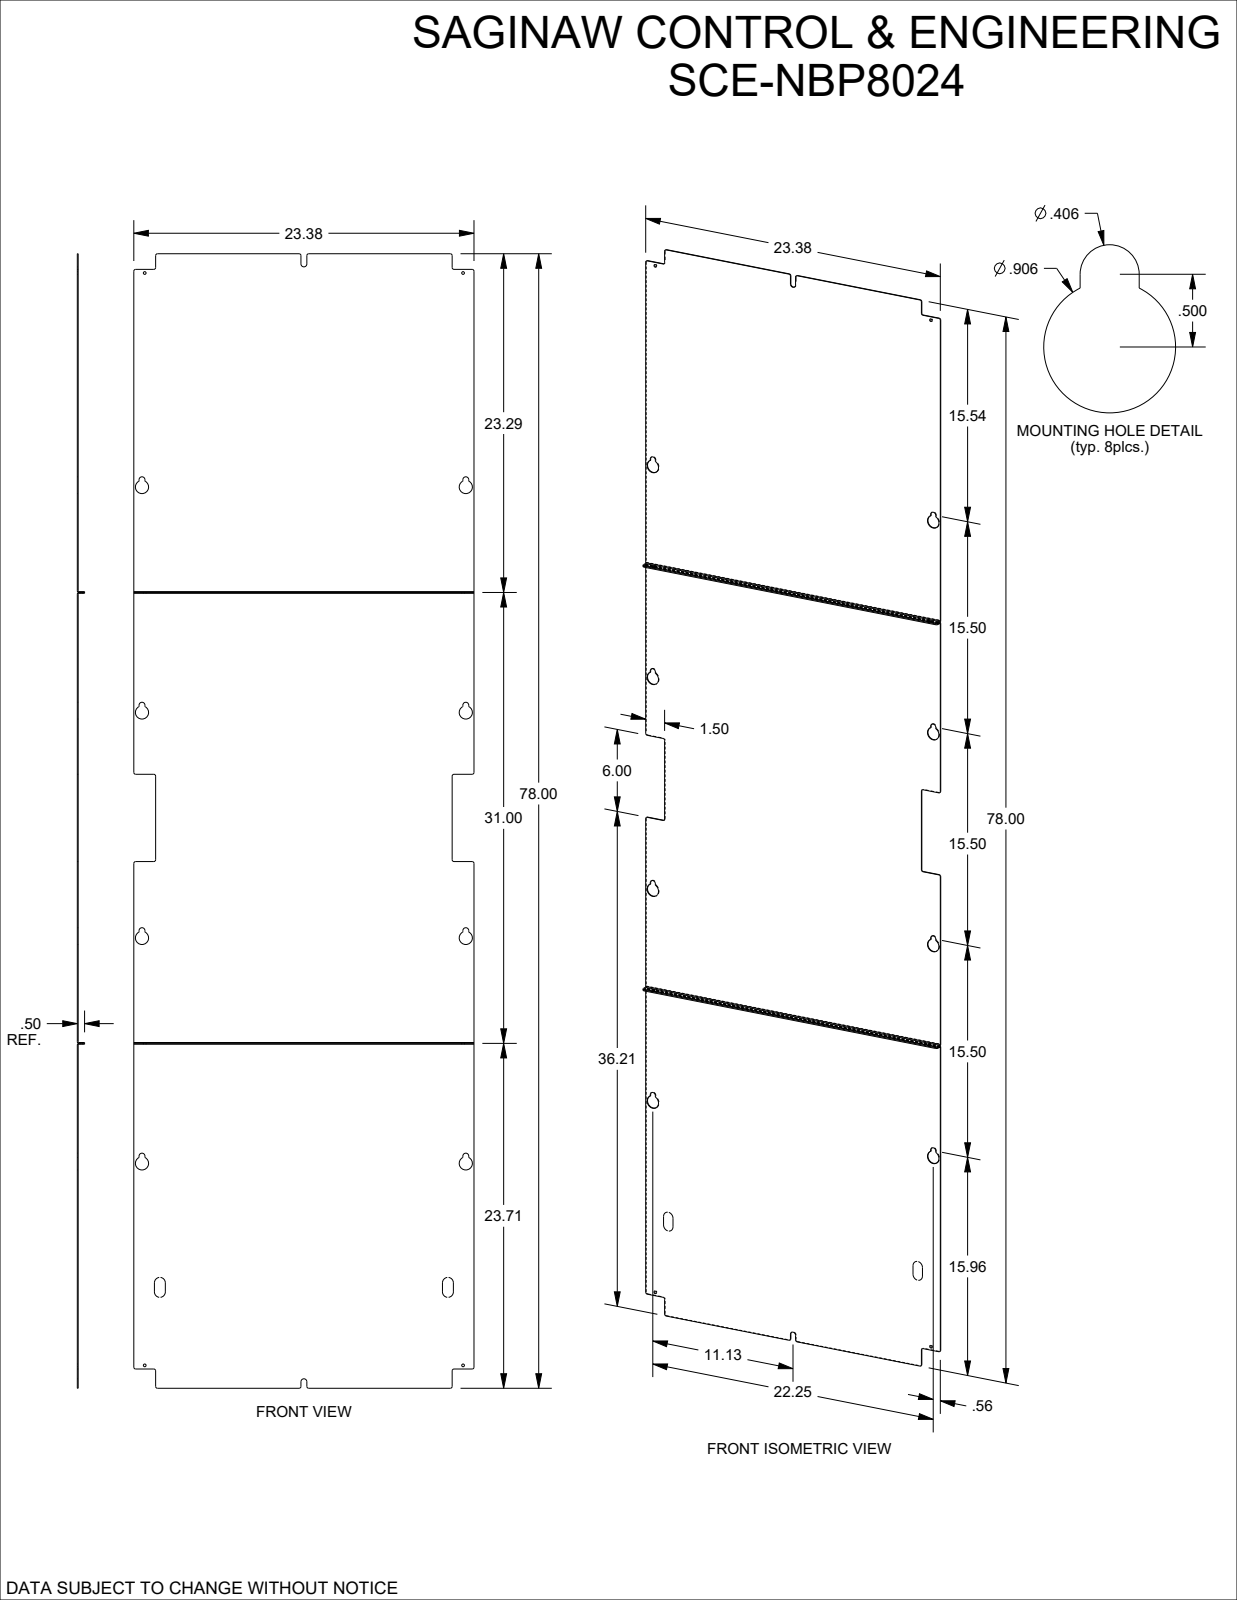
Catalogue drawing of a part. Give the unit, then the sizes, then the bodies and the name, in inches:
Units: inches
Overall size (bounding box): 78 × 23.375 × 0.5
Round holes (diameter × count): ⌀0.906 ×8, ⌀0.188 ×6
Partial cylindrical surfaces — rounded edges, fillets, slot ends (radius × count): R0.125 ×26, R0.03 ×12, R0.203 ×10, R0.052 ×4, R0.112 ×4
Main face-to-face distances: 0.06, 31, 0.06, 0.12, 31.06, 31.12, 31.06, 30.94, 30.94, 30.88
Hole centre spacings: 15.5, 27.117, 22.25, 31, 38.159, 21.875, 13.888, 14.714
Volume: 109.7 in³ · Surface area: 3 678 in²
Bodies: 3 solids, 174 faces (80 planar, 94 cylindrical, 0 other)
Part name (STEP PRODUCT): SCE-NBP8024
STEP written by: SolidWorks 2023 (AUTOMOTIVE_DESIGN)
